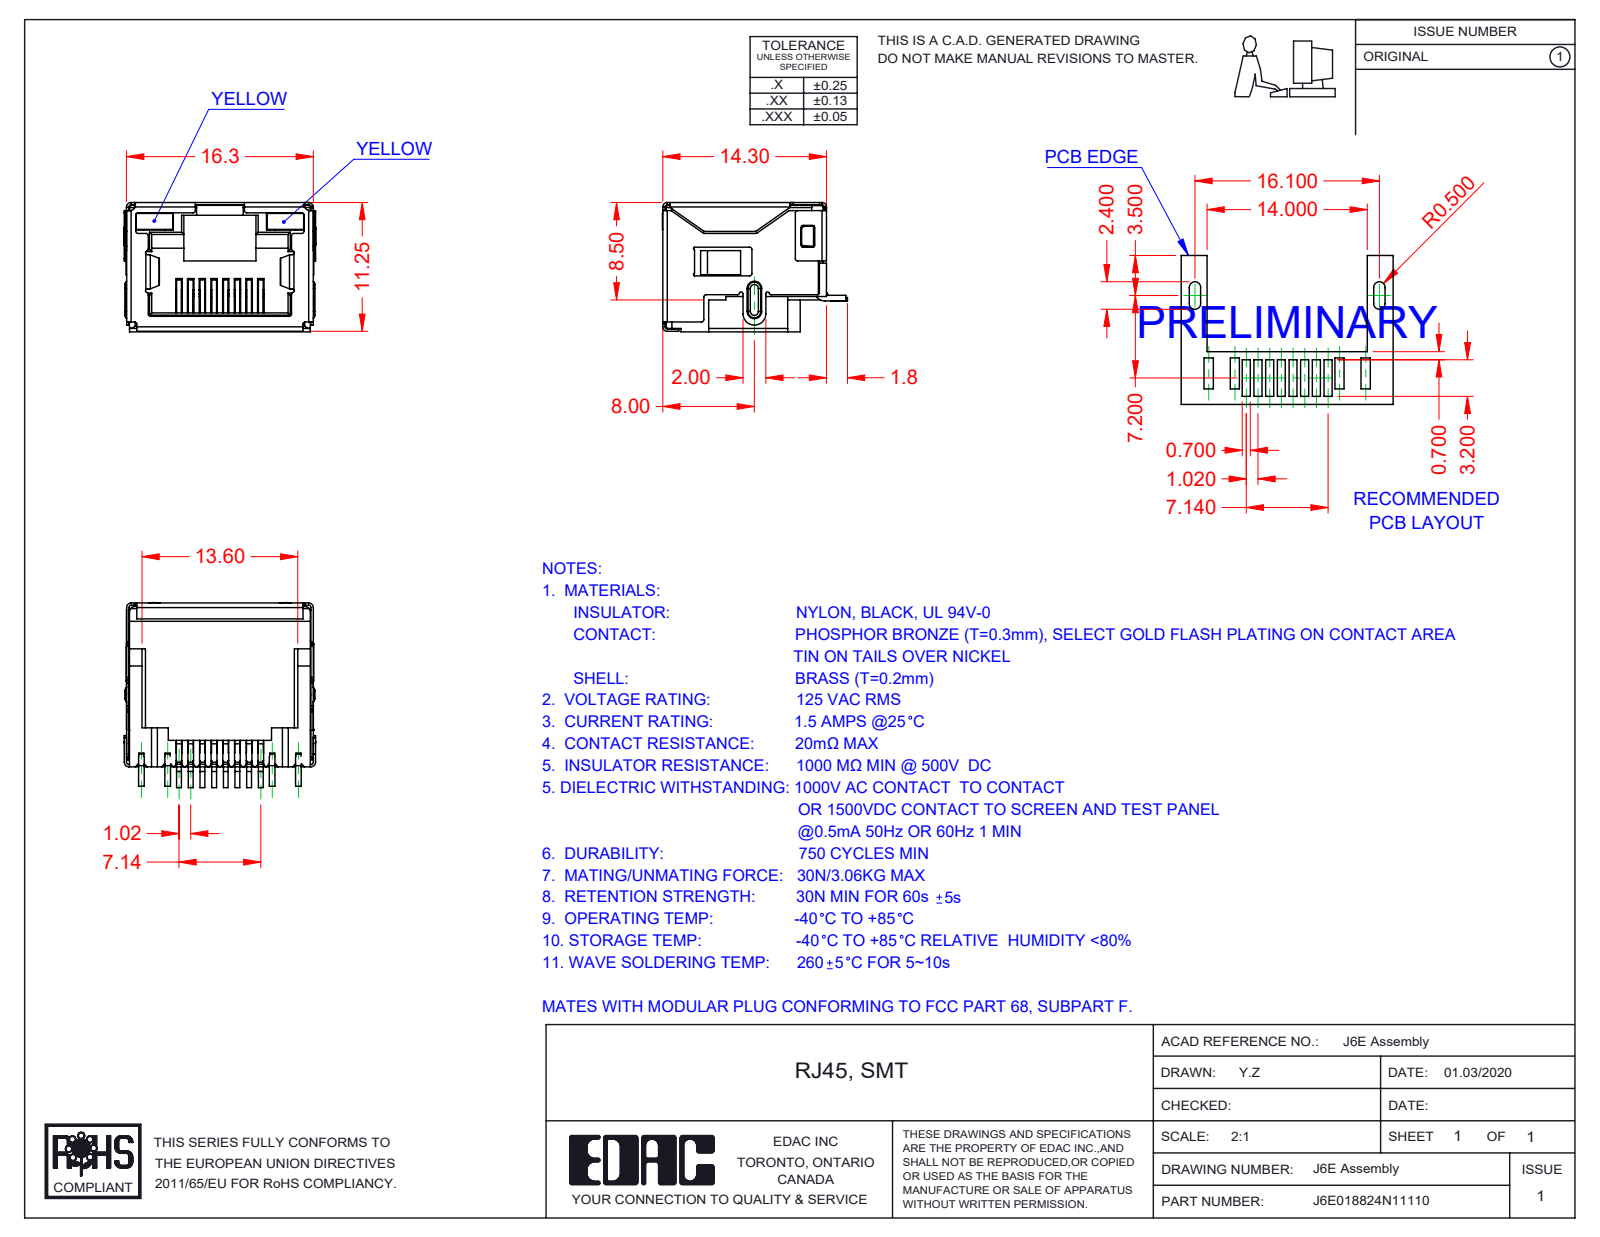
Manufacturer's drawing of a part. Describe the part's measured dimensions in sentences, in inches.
The part is named "6E Shield_LED; 6E LED RH_1-Yellow; 6E Insulator_LED; J6E018824N11110 (+2 more)". Its 3-D file was written by "SolidWorks 2016 (CONFIG_CONTROL_DESIGN)". It is 12 solids with 1496 faces: 1099 planar, 347 cylindrical and 50 other. Overall it measures 0.659 by 0.636 by 0.445 inches. Its volume is 0.068 cubic inches and its surface area 6.27 square inches. Partial cylindrical surfaces (rounded edges, fillets, slot ends): 82 of radius 0.008, 17 of radius 0.01, 13 of radius 0.016, 13 of radius 0.02, 10 of radius 0.004, 7 of radius 0.006, 4 of radius 0.012, 3 of radius 0.039. The main face-to-face distances are 0.435, 0.632, 0.634, 0.624, 0.437, 0.445, 0.094, 0.028, 0.388, 0.019.
